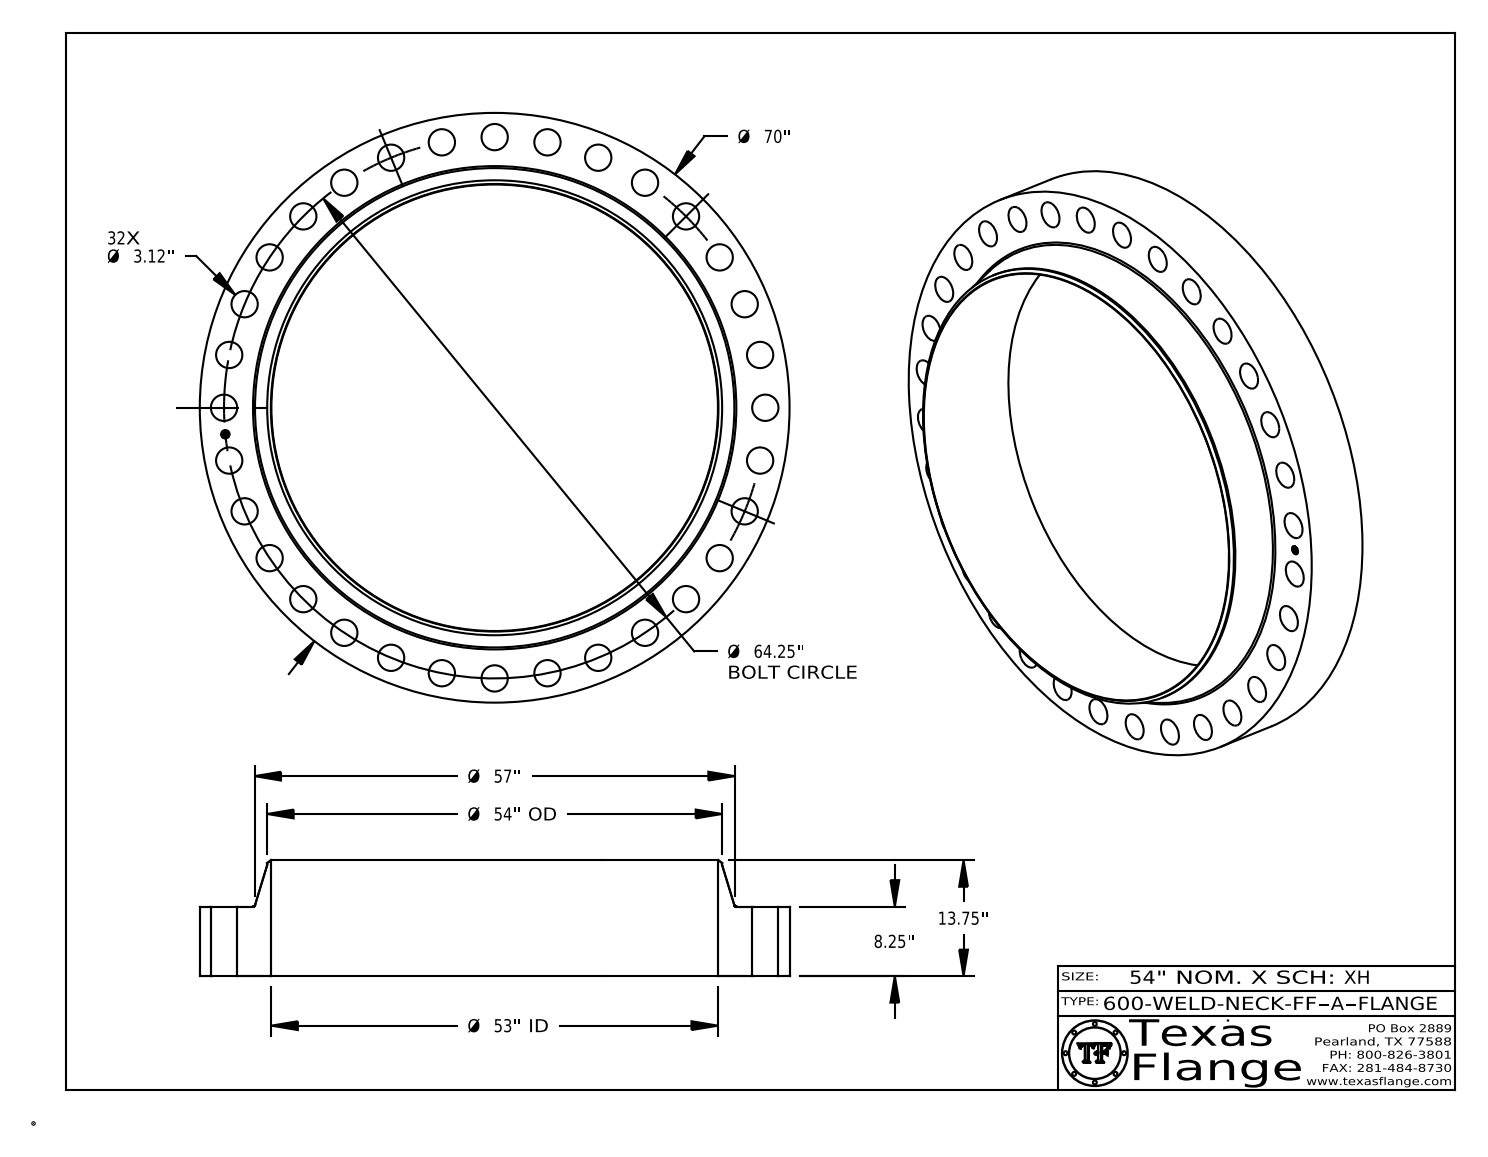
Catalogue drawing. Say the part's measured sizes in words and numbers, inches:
The part is named "600-WELD-NECK-FF, Series A". Its 3-D file was written by "CATIA V5 STEP AP214 (AUTOMOTIVE_DESIGN)". It is 1 solid with 464 faces: 368 planar, 90 cylindrical and 6 other. Overall it measures 70 by 70 by 13.75 inches. Its volume is 12 620 cubic inches and its surface area 10 173 square inches. Round holes: 32 of diameter 3.12, 1 of diameter 1, 1 of diameter 53. Round bosses or shafts: 8 of diameter 0.061, 1 of diameter 70, 1 of diameter 54, 1 of diameter 0.788. The main face-to-face distances are 8.25, 13.75, 5.5, 0.015, 8.235, 5.515, 0.298, 0.293, 0.054, 0.193. The hole center spacings are 12.535, 6.298, 18.651, 24.587, 40.76, 61.483, 63.941, 45.431.
